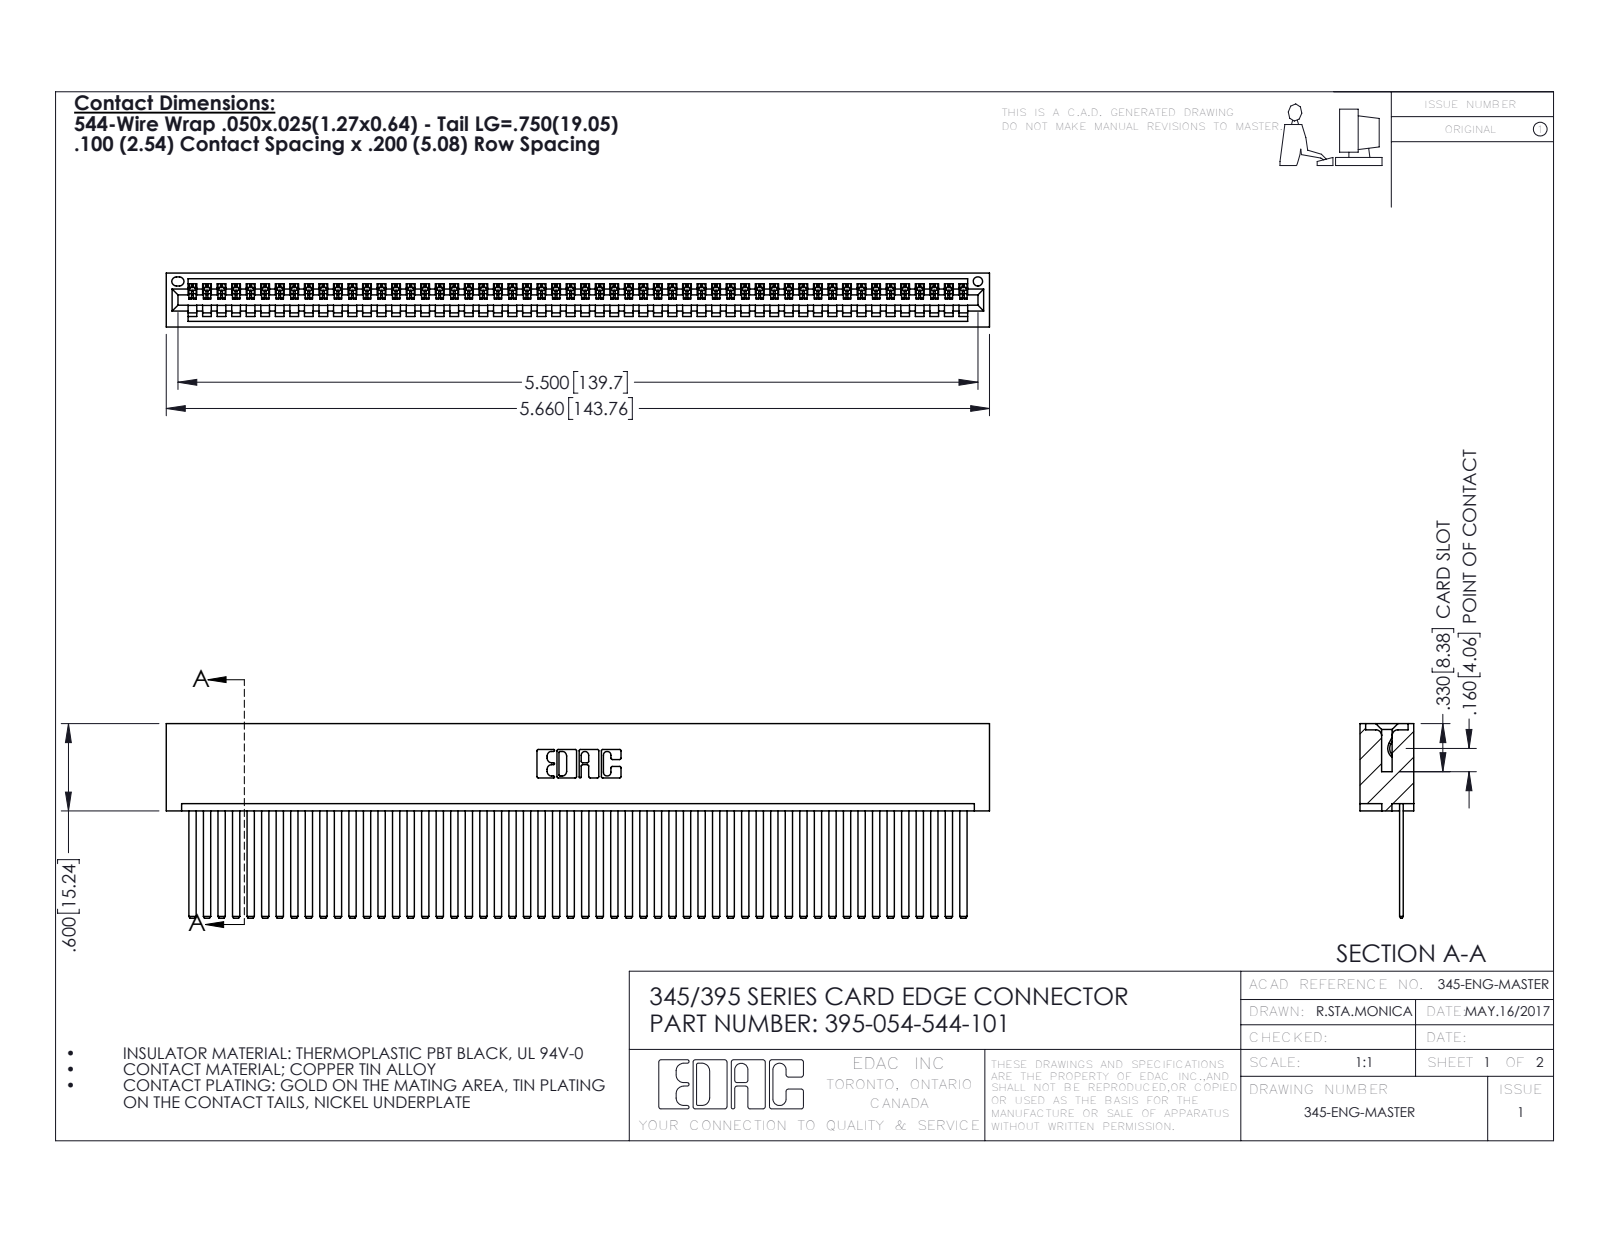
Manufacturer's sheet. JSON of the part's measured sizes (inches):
{"part_name": "345 Part_No Mounting Lugs; 395-054-544-101; 345-292-001_345-293-144", "step_written_by": "SolidWorks 2016 (CONFIG_CONTROL_DESIGN)", "units": "inches", "bodies": {"solids": 55, "faces": 2926, "planar": 2020, "cylindrical": 906, "other": 0}, "overall_size": [5.66, 1.337, 0.37], "volume_in3": 0.913, "surface_area_in2": 34.28, "round_holes": [[0.064, 1]], "partial_cylinders_radius": [[0.006, 108], [0.01, 22], [0.007, 6], [0.031, 6], [0.026, 3], [0.031, 2], [0.04, 2], [0.014, 1]], "face_to_face_distances": [0.072, 0.298, 0.025, 0.098, 0.272, 0.37, 0.2, 0.225, 0.149, 0.072]}
